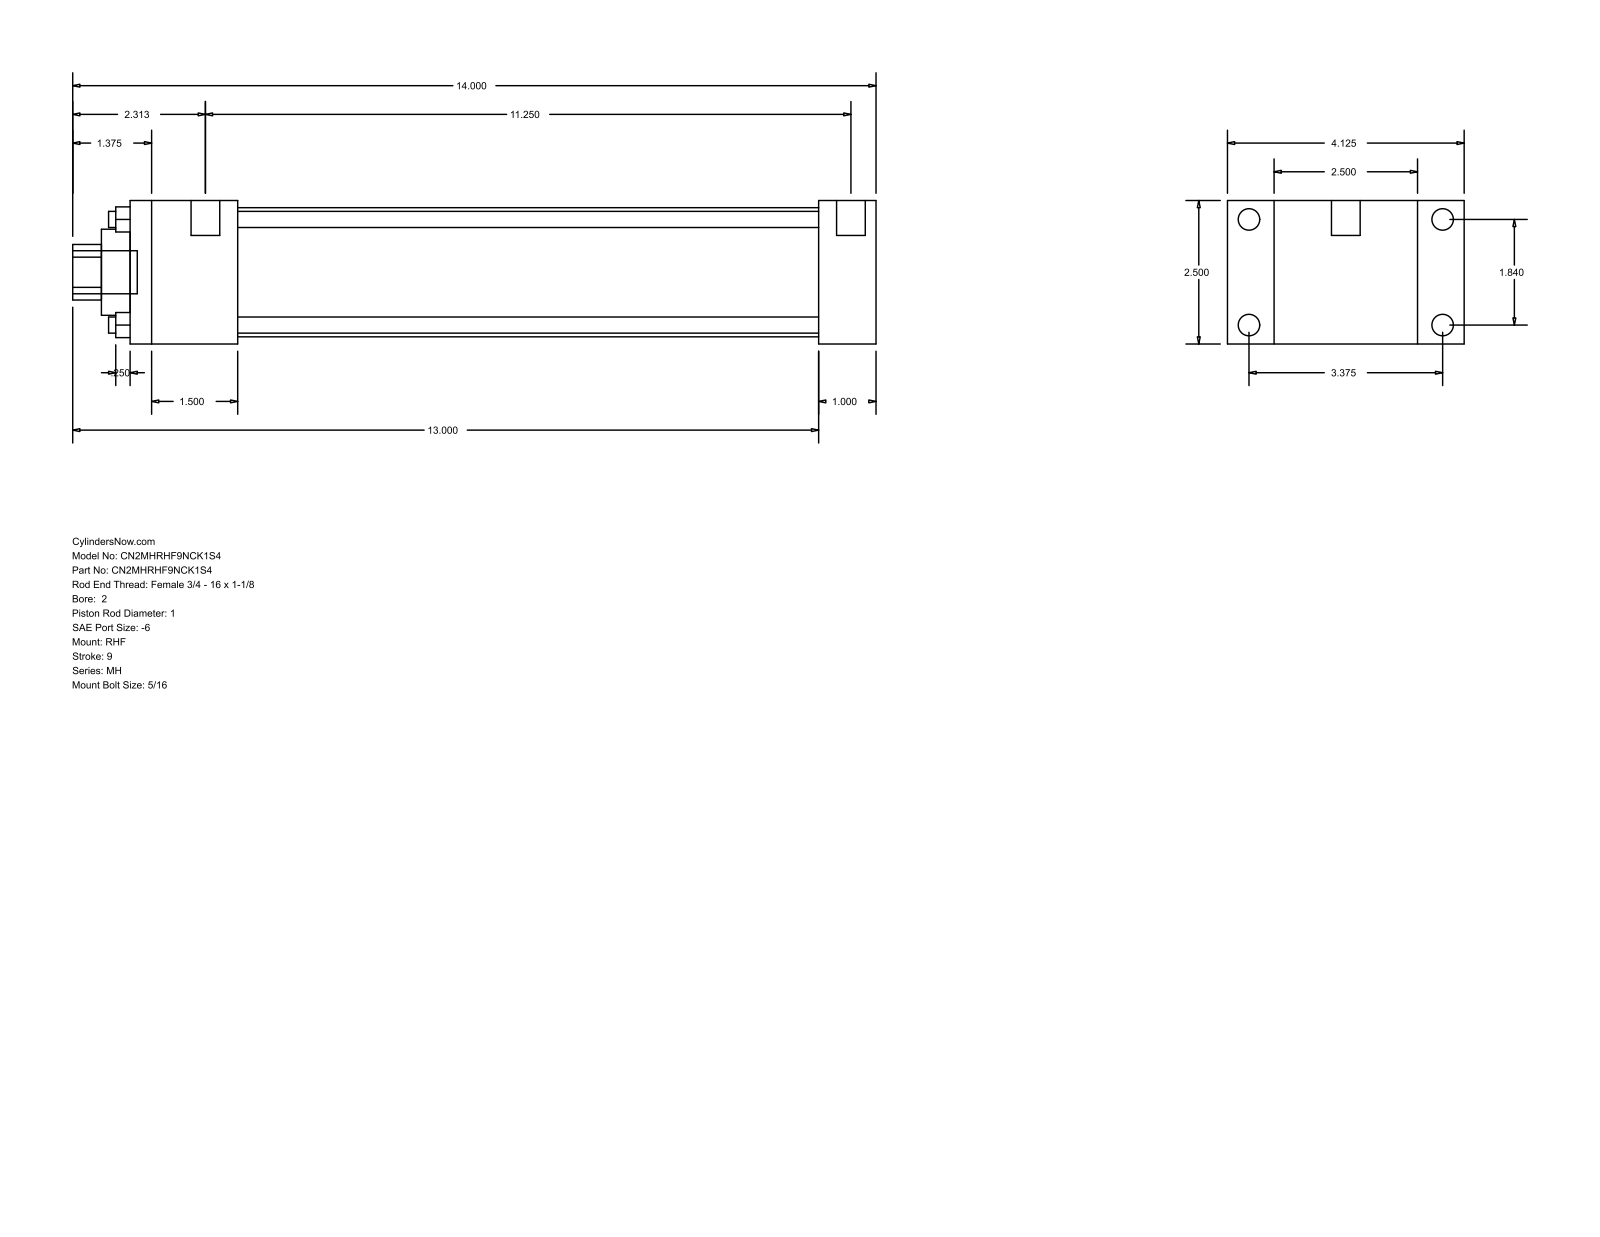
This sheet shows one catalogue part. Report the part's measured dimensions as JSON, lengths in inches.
{"part_name": "MH_RHF__0200_1", "step_written_by": "GSSL Pune (CONFIG_CONTROL_DESIGN)", "units": "inches", "bodies": {"solids": 0, "faces": 88, "planar": 60, "cylindrical": 28, "other": 0}, "overall_size": [14, 4.125, 2.5], "round_holes": [[0.281, 4], [1, 1], [1.5, 1], [2.25, 1]], "round_bosses_or_shafts": [[0.375, 4], [0.219, 4], [0.5, 2], [0.75, 1]], "partial_cylinders_radius": [[0.484, 1]], "face_to_face_distances": [2.5, 1, 0.813, 3.313, 13, 12, 4.125, 1.875, 10.125, 11.125], "hole_center_spacings": [1.301, 1.84, 2.602]}
